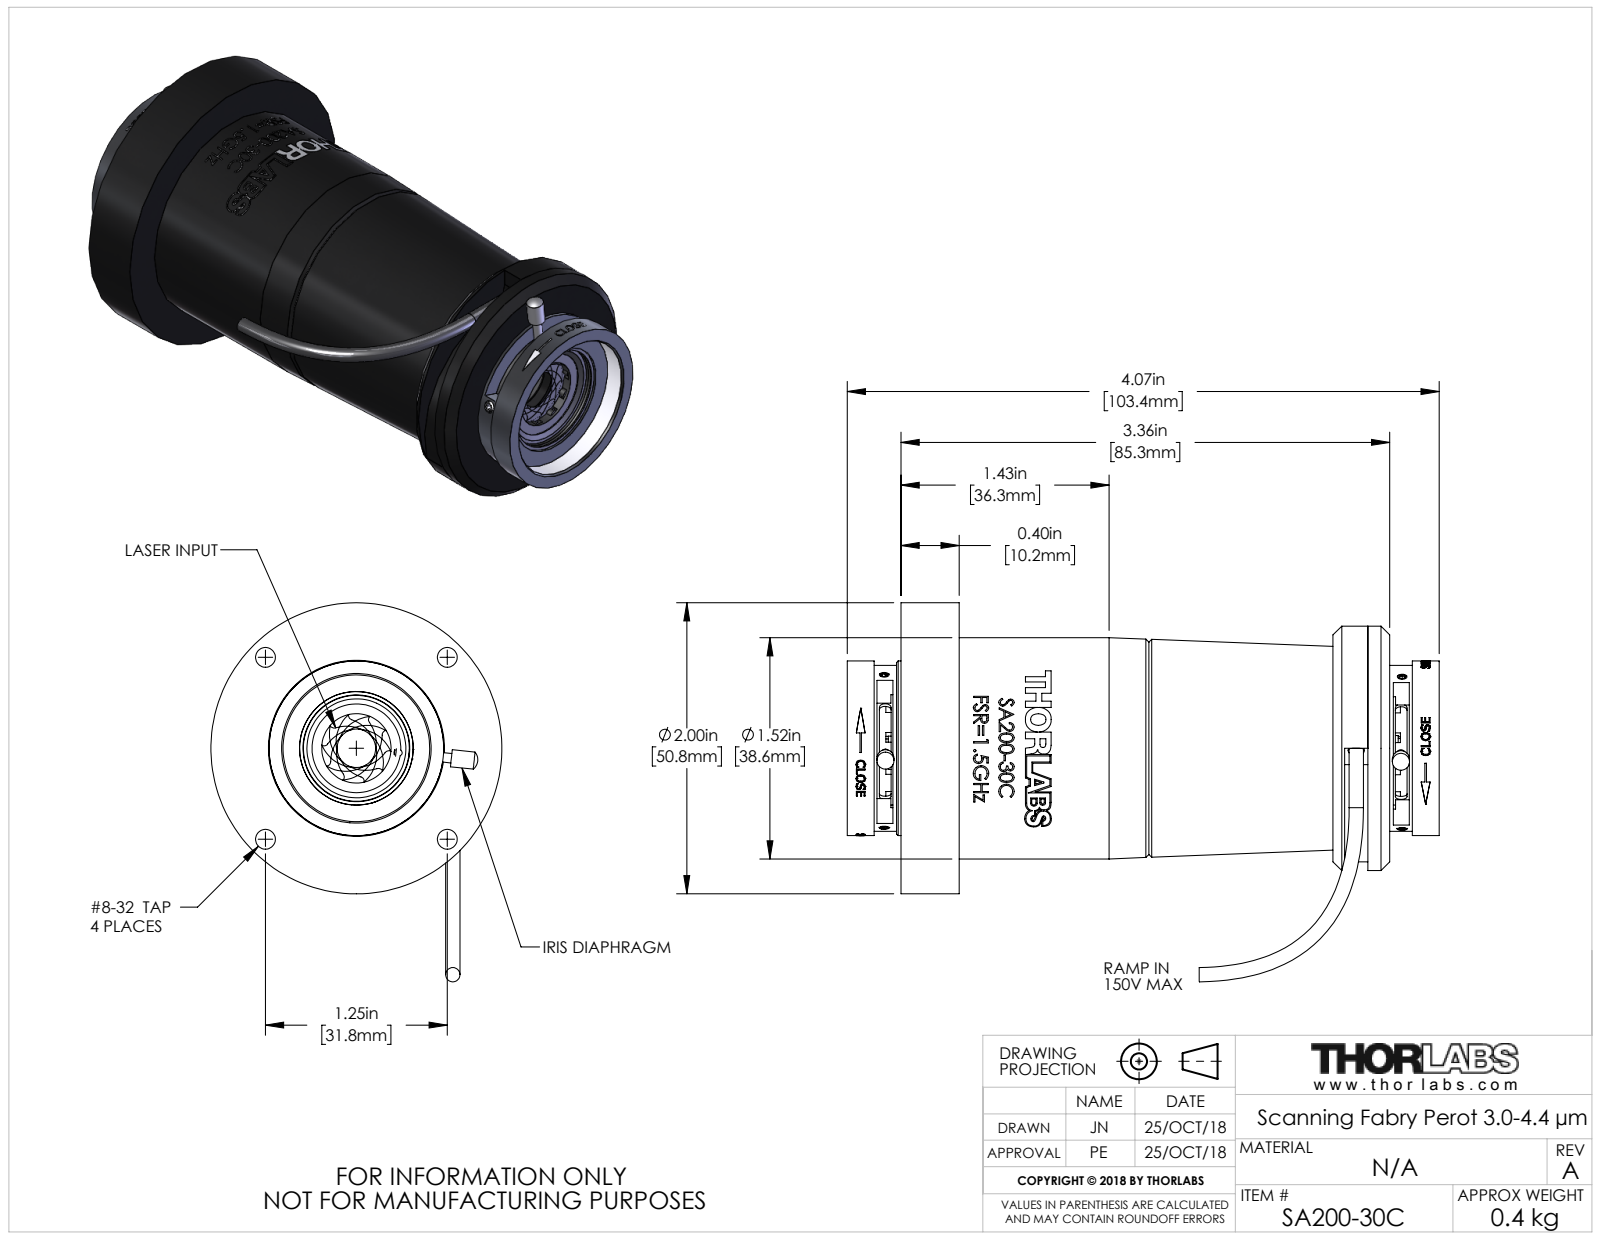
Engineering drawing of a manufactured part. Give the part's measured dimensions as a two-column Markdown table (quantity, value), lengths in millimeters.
| quantity | value |
| --- | --- |
| part name | STN051656-E0W |
| STEP written by | SolidWorks 2018 (AUTOMOTIVE_DESIGN) |
| units | millimeters |
| bodies | 38 solids, 1469 faces (579 planar, 494 cylindrical, 396 other) |
| overall size | 103.38 × 66.16 × 50.8 |
| volume | 62 085 mm³ |
| surface area | 55 338 mm² |
| round holes (diameter × count) | 1.68 × 20, 3.45 × 4, 1.1 × 2, 1.6 × 2, 2.87 × 1, 10.16 × 1, 12.04 × 1, 12.12 × 1, 15.49 × 1, 18.63 × 1, 18.8 × 1, 19.84 × 1 |
| round bosses / shafts (diameter × count) | 1.65 × 22, 1.52 × 20, 2.18 × 4, 2.98 × 2, 1.63 × 2, 50.8 × 1, 42.67 × 1, 38.61 × 1 |
| partial cylindrical surfaces (radius × count) | 0.83 × 20, 0.85 × 20, 1.61 × 20, 6.38 × 20, 9.6 × 20, 0.62 × 2, 3.3 × 2, 25.4 × 2 |
| main face-to-face distances | 81.53, 2.03, 1.27, 86.81, 85.34, 0.76, 3.81, 76.2, 0.38, 86.48 |
| hole center spacings | 14.11, 12, 7.42, 4.59, 8.72, 14.83, 14.84, 4.51 |
